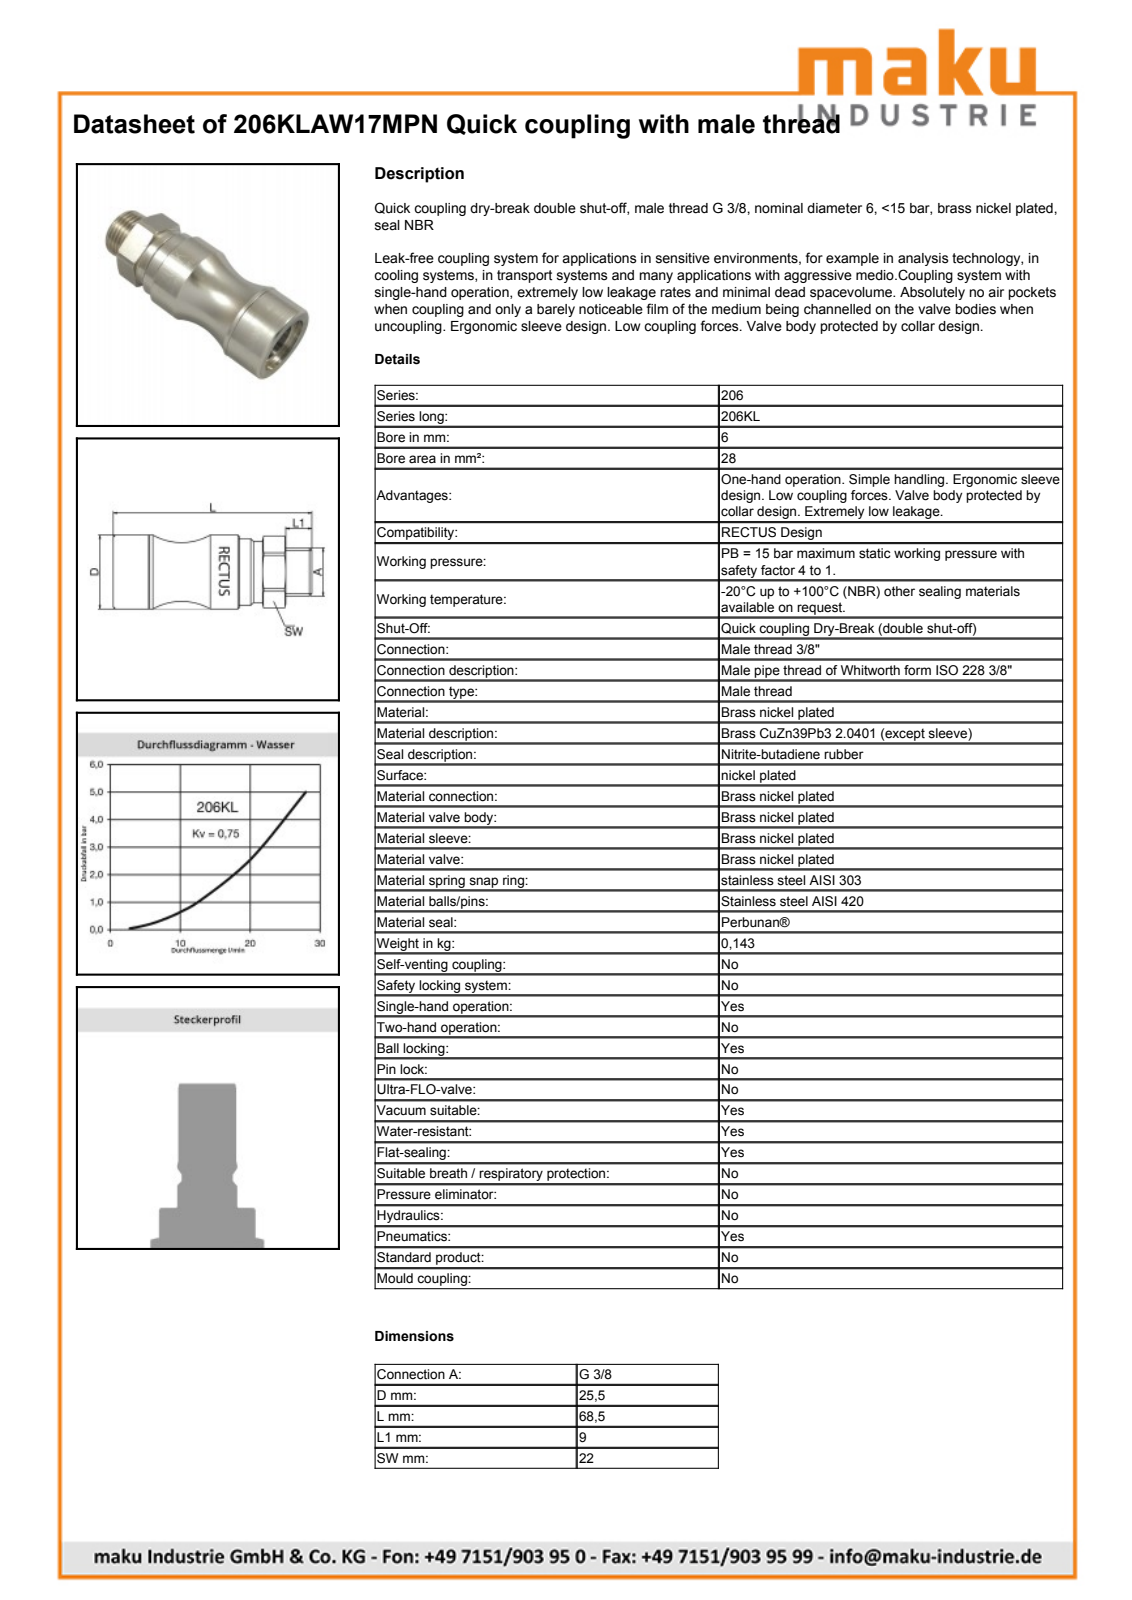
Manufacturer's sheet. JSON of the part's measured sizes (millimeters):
{"part_name": "D108799", "step_written_by": "Autodesk Inventor 2013 (AUTOMOTIVE_DESIGN)", "units": "millimeters", "bodies": {"solids": 1, "faces": 1023, "planar": 353, "cylindrical": 133, "other": 537}, "overall_size": [68.5, 25.5, 25.5], "volume_mm3": 23548, "surface_area_mm2": 16303, "round_holes": [[13.75, 1], [14.45, 1], [15.65, 1], [17, 1], [18.1, 1], [18.15, 1], [18.25, 1], [20.05, 1], [21.2, 1], [21.3, 1], [23.1, 1], [23.55, 1]], "round_bosses_or_shafts": [[25.5, 1], [25.3, 1], [23.4, 1], [23, 1], [21, 1], [20, 1], [18, 1], [16.66, 1]], "partial_cylinders_radius": [[12.4, 1]], "face_to_face_distances": [22, 68.5, 59.5, 9, 1.3, 58.2, 67.2, 21.98, 4.65, 47.4]}
